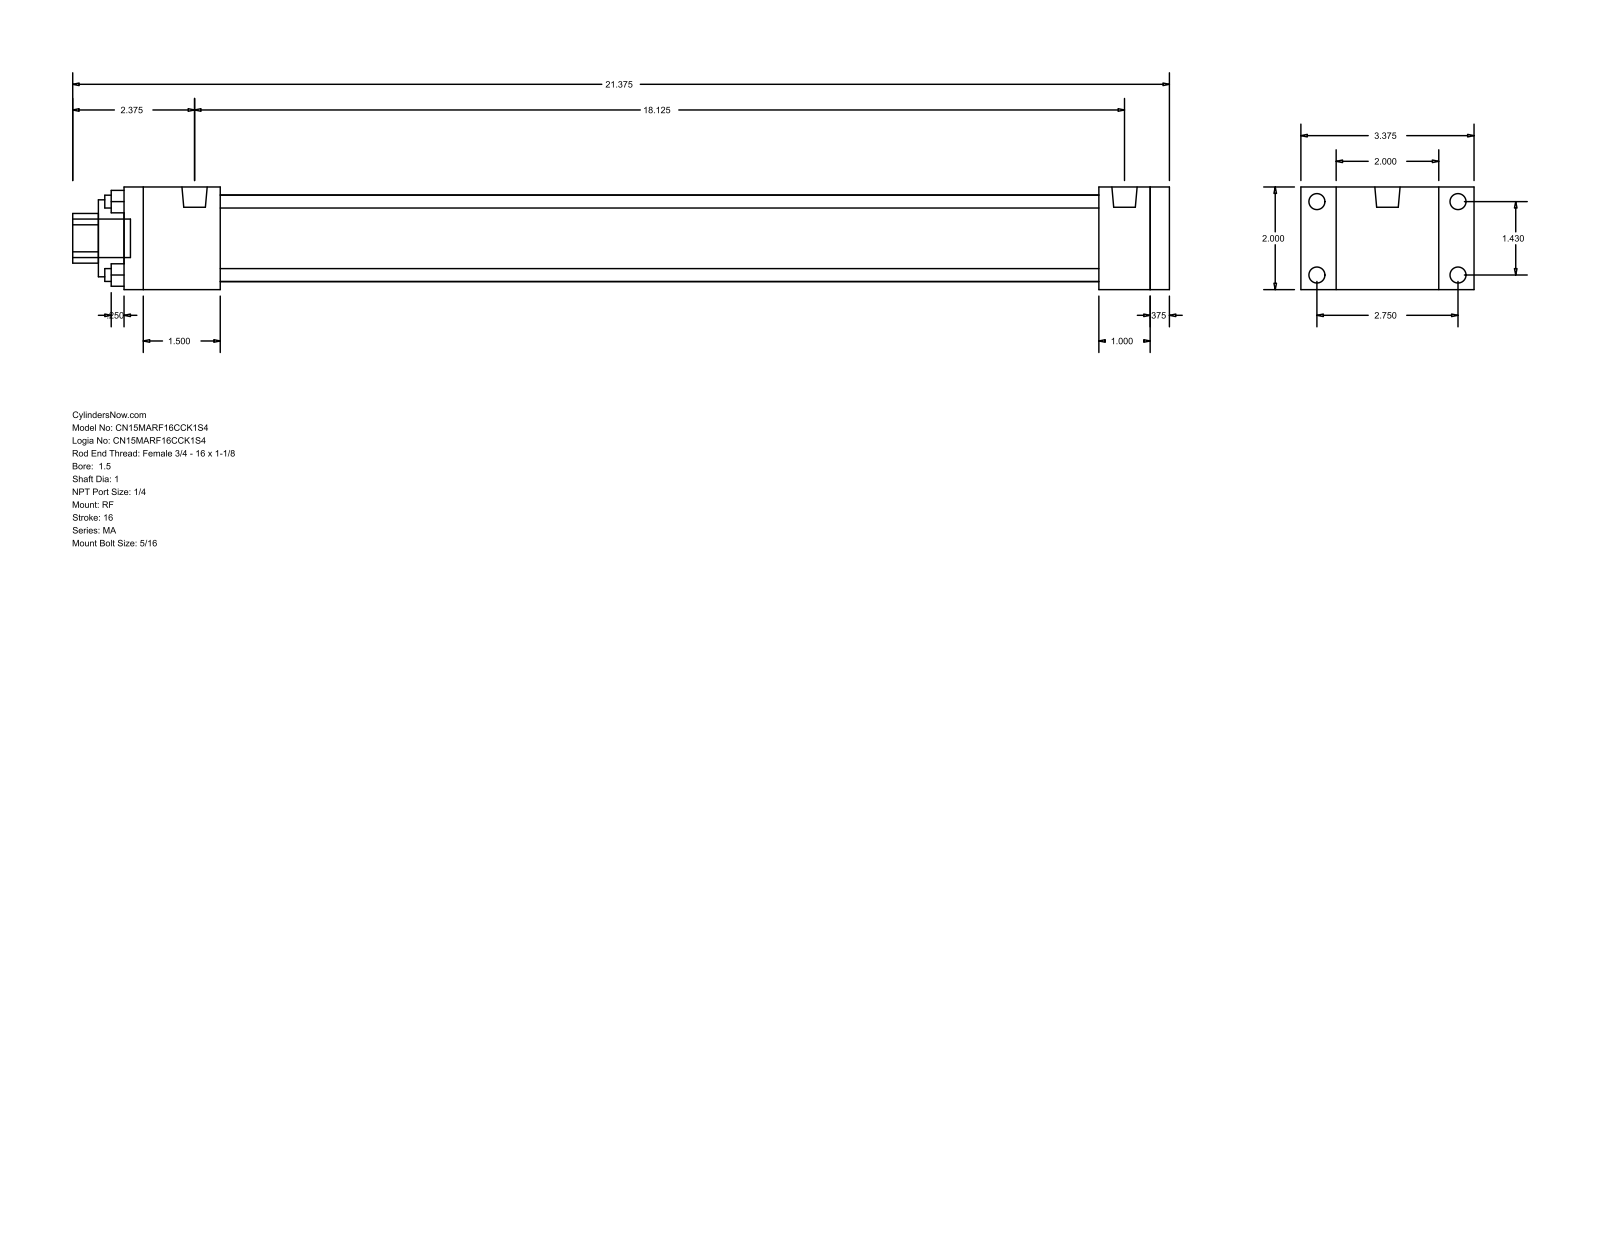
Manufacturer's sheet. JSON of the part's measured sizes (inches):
{"part_name": "MA_RF__0150_1", "step_written_by": "GSSL Pune (CONFIG_CONTROL_DESIGN)", "units": "inches", "bodies": {"solids": 0, "faces": 92, "planar": 64, "cylindrical": 28, "other": 0}, "overall_size": [21.375, 3.375, 2], "round_holes": [[0.25, 4], [1, 1], [1.5, 1], [1.69, 1]], "round_bosses_or_shafts": [[0.313, 8], [0.492, 2], [0.75, 1]], "partial_cylinders_radius": [[0.484, 1]], "face_to_face_distances": [2, 0.375, 20.375, 20, 1, 19, 1.375, 1.875, 17.125, 18.125], "hole_center_spacings": [1.011, 1.43, 2.022]}
